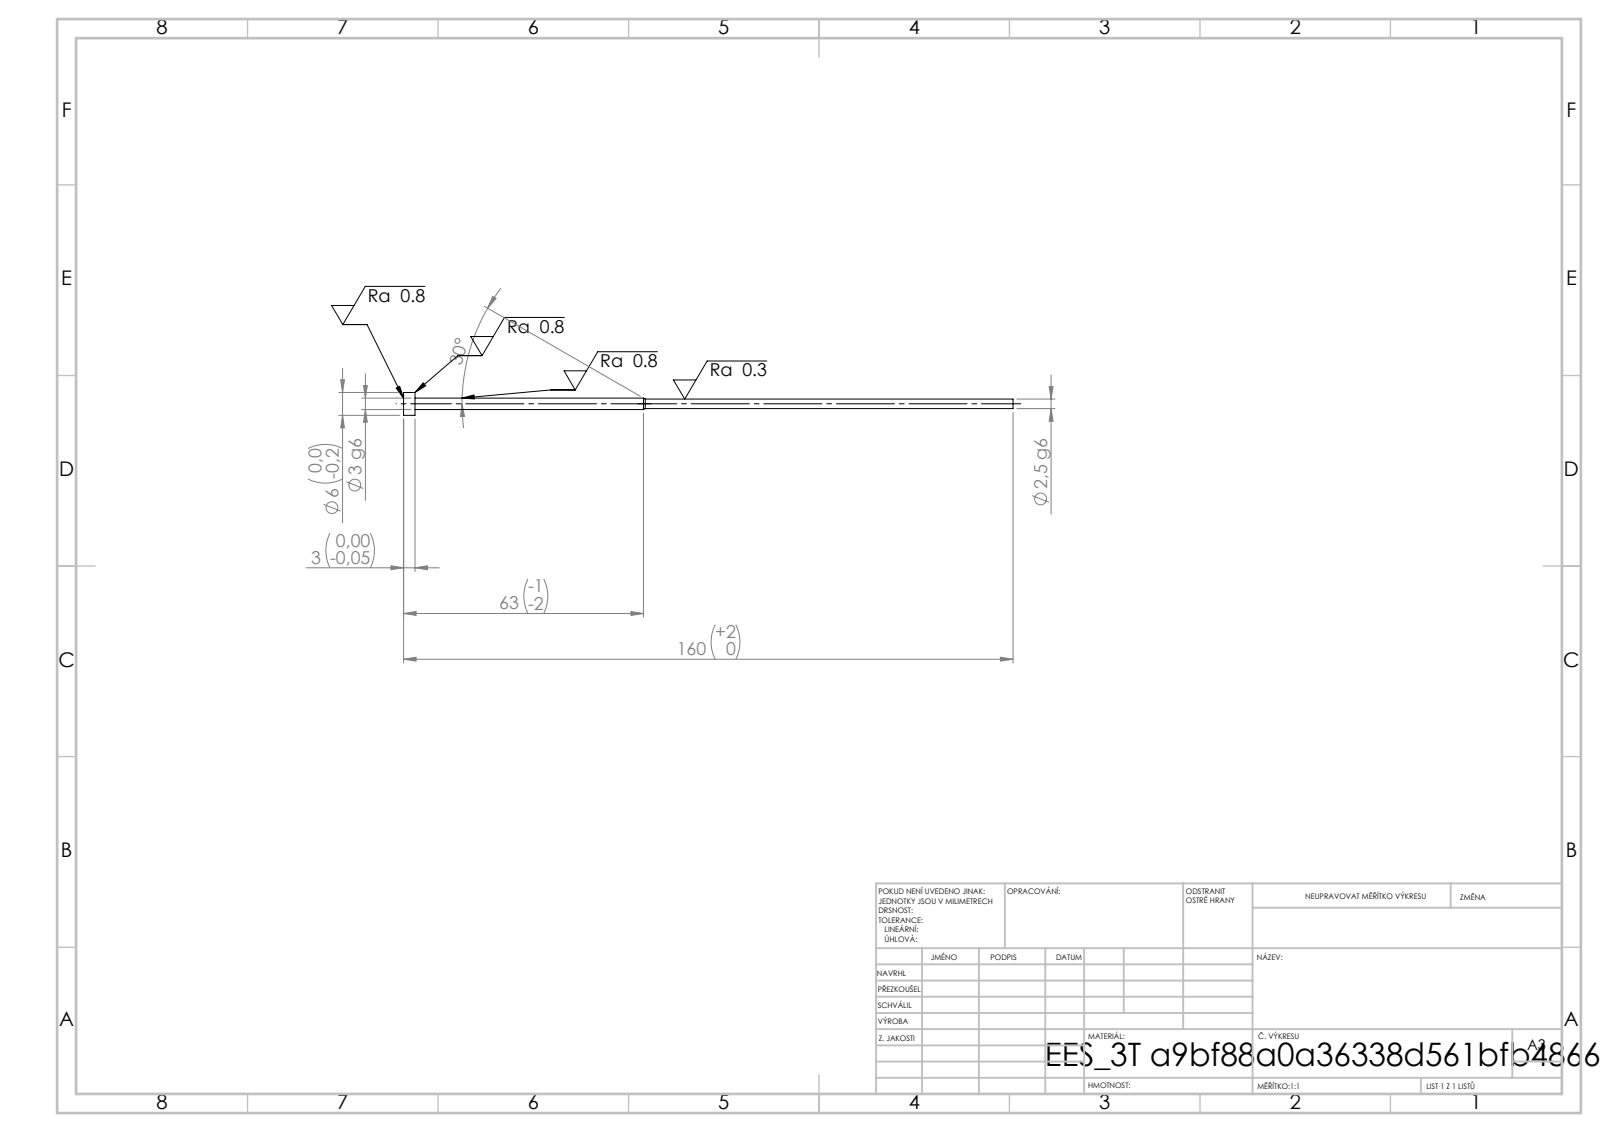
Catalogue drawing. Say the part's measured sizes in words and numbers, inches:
Its 3-D file was written by "SolidWorks 2019 (CONFIG_CONTROL_DESIGN)". It is 1 solid with 11 faces: 3 planar, 6 cylindrical and 2 other. Overall it measures 6.299 by 0.236 by 0.236 inches. Its volume is 0.06 cubic inches and its surface area 2.23 square inches. Round bosses or shafts: 1 of diameter 0.236, 1 of diameter 0.118, 1 of diameter 0.098. The main face-to-face distances are 0.118, 6.181, 6.299.
